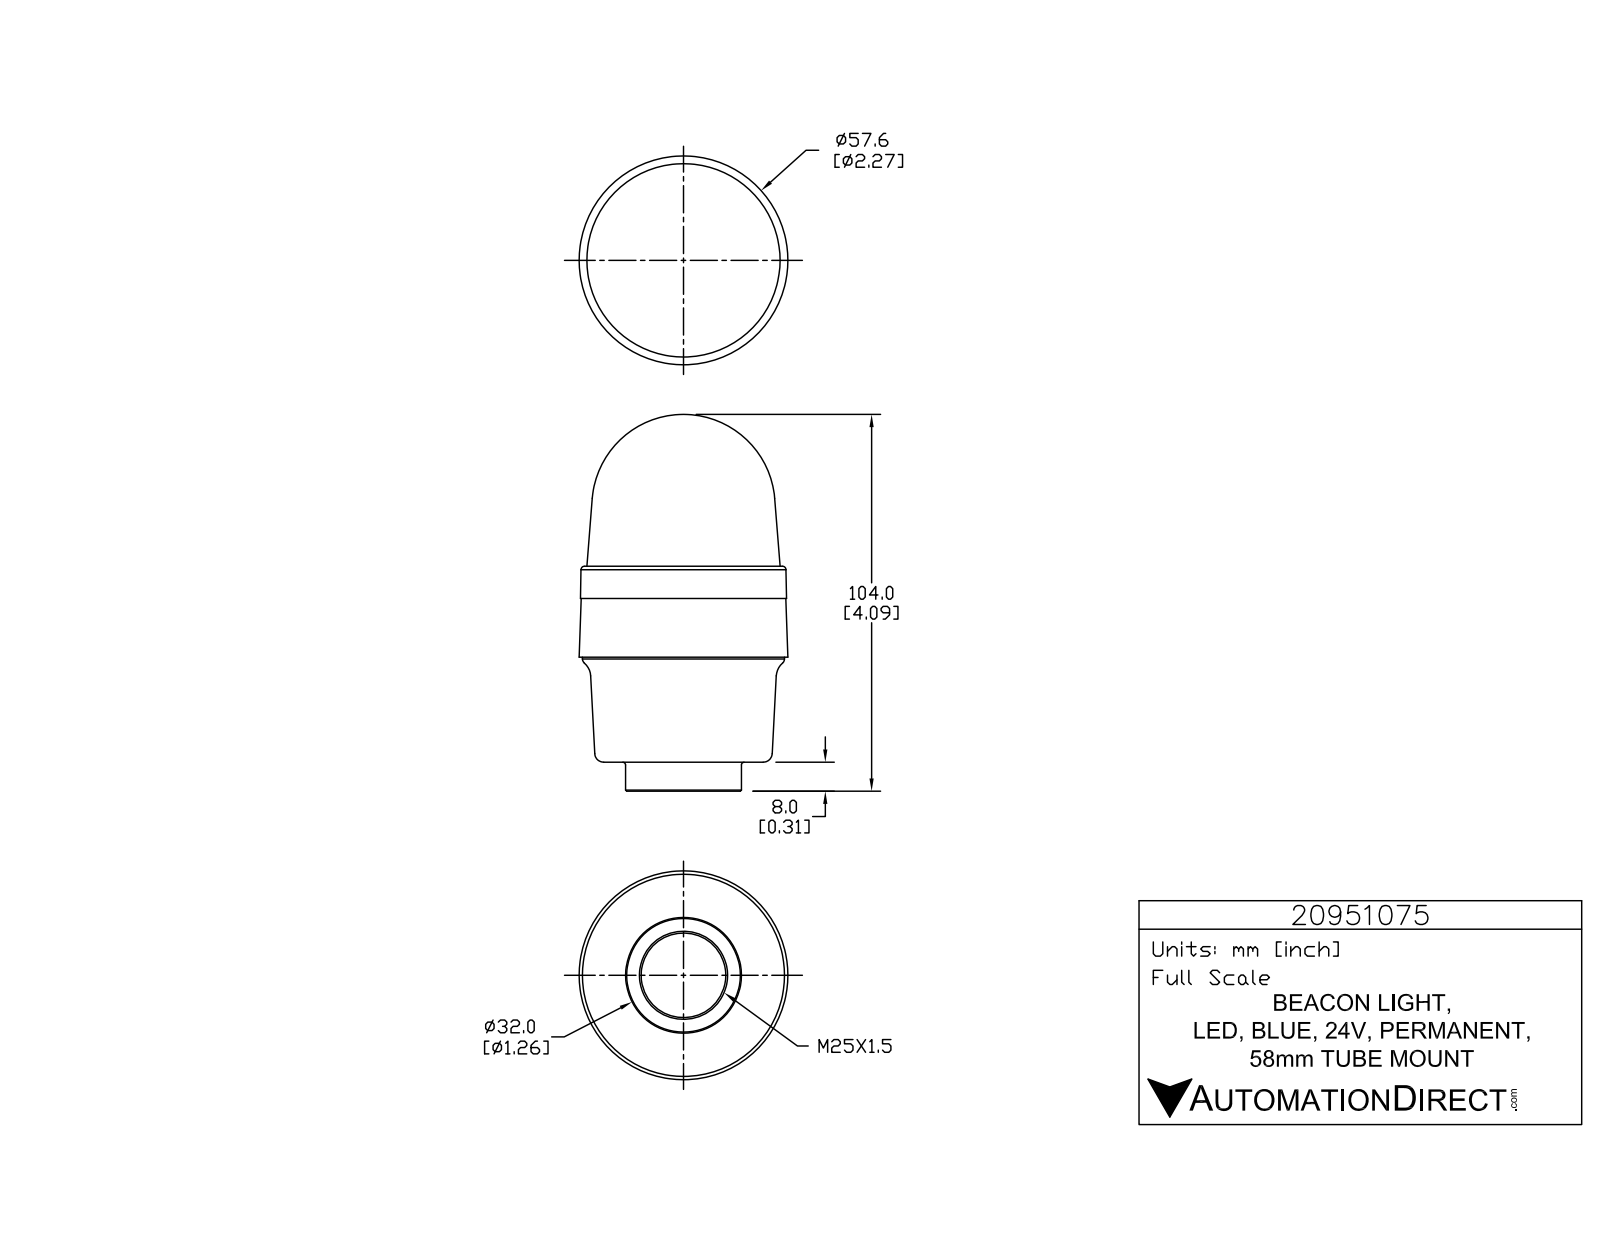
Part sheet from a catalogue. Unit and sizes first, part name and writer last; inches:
Units: inches
Overall size (bounding box): 4.051 × 2.269 × 2.269
Round holes (diameter × count): ⌀0.039 ×3, ⌀0.92 ×1
Round bosses / shafts (diameter × count): ⌀0.226 ×3, ⌀0.056 ×3, ⌀2.197 ×1, ⌀1.26 ×1
Partial cylindrical surfaces — rounded edges, fillets, slot ends (radius × count): R0.008 ×6, R0.008 ×6, R0.008 ×6, R0.131 ×6, R0.004 ×3, R0.005 ×3, R0.008 ×3, R0.008 ×3
Main face-to-face distances: 0.315, 1.142, 1.457, 0.988, 2.13, 2.445, 0.35, 0.638, 1.78, 2.094
Volume: 11.72 in³ · Surface area: 29.93 in²
Bodies: 1 solid, 791 faces (525 planar, 168 cylindrical, 98 other)
Part name (STEP PRODUCT): 20951075
STEP written by: SolidWorks 2015 (AUTOMOTIVE_DESIGN)
